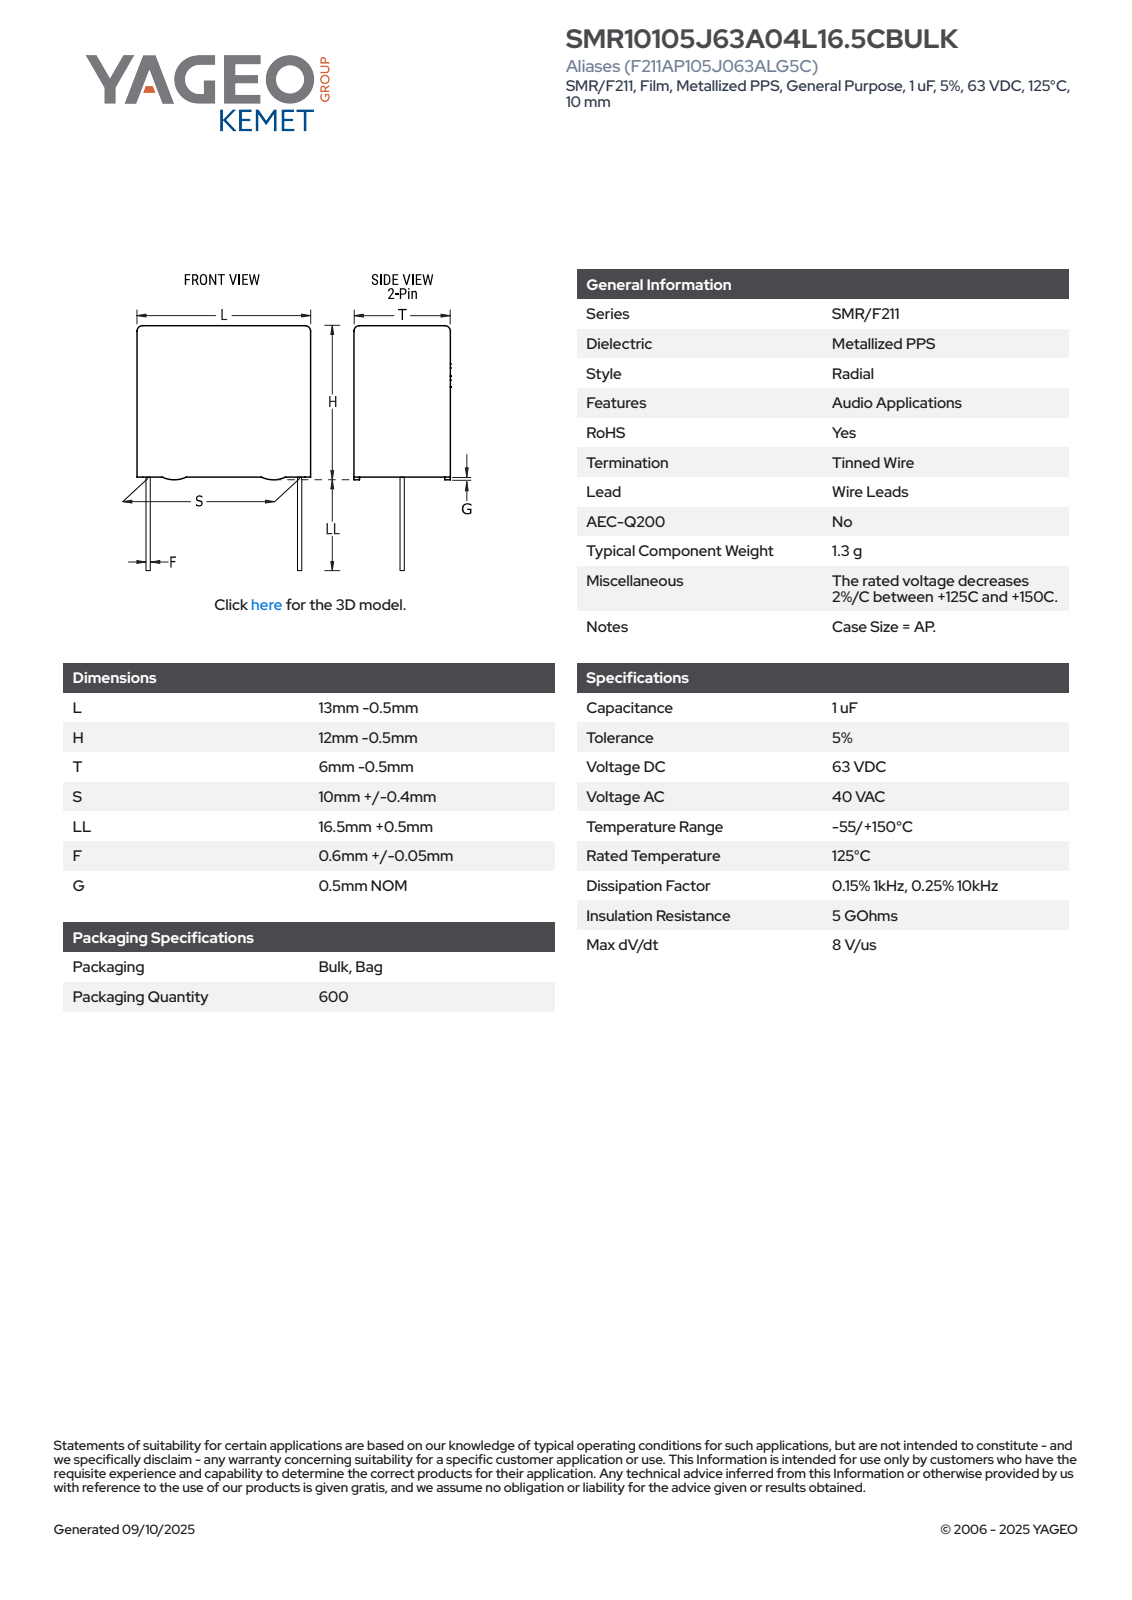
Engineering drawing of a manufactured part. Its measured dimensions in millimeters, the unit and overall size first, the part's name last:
Units: millimetres
Overall size (bounding box): 28.5 × 12.5 × 5.5
Round bosses / shafts (diameter × count): ⌀0.65 ×2
Partial cylindrical surfaces — rounded edges, fillets, slot ends (radius × count): R0.5 ×4
Main face-to-face distances: 5.5, 12.5, 11, 0.31, 5.19, 0.5, 11.5, 4.88, 17, 17.5
Volume: 767 mm³ · Surface area: 623 mm²
Bodies: 4 solids, 89 faces (81 planar, 8 cylindrical, 0 other)
Part name (STEP PRODUCT): CFR_RBG_13X12X6_L12.5H11.5T5.5S10LL17F0.65G0.5
STEP written by: SolidWorks 2014 (AUTOMOTIVE_DESIGN)
